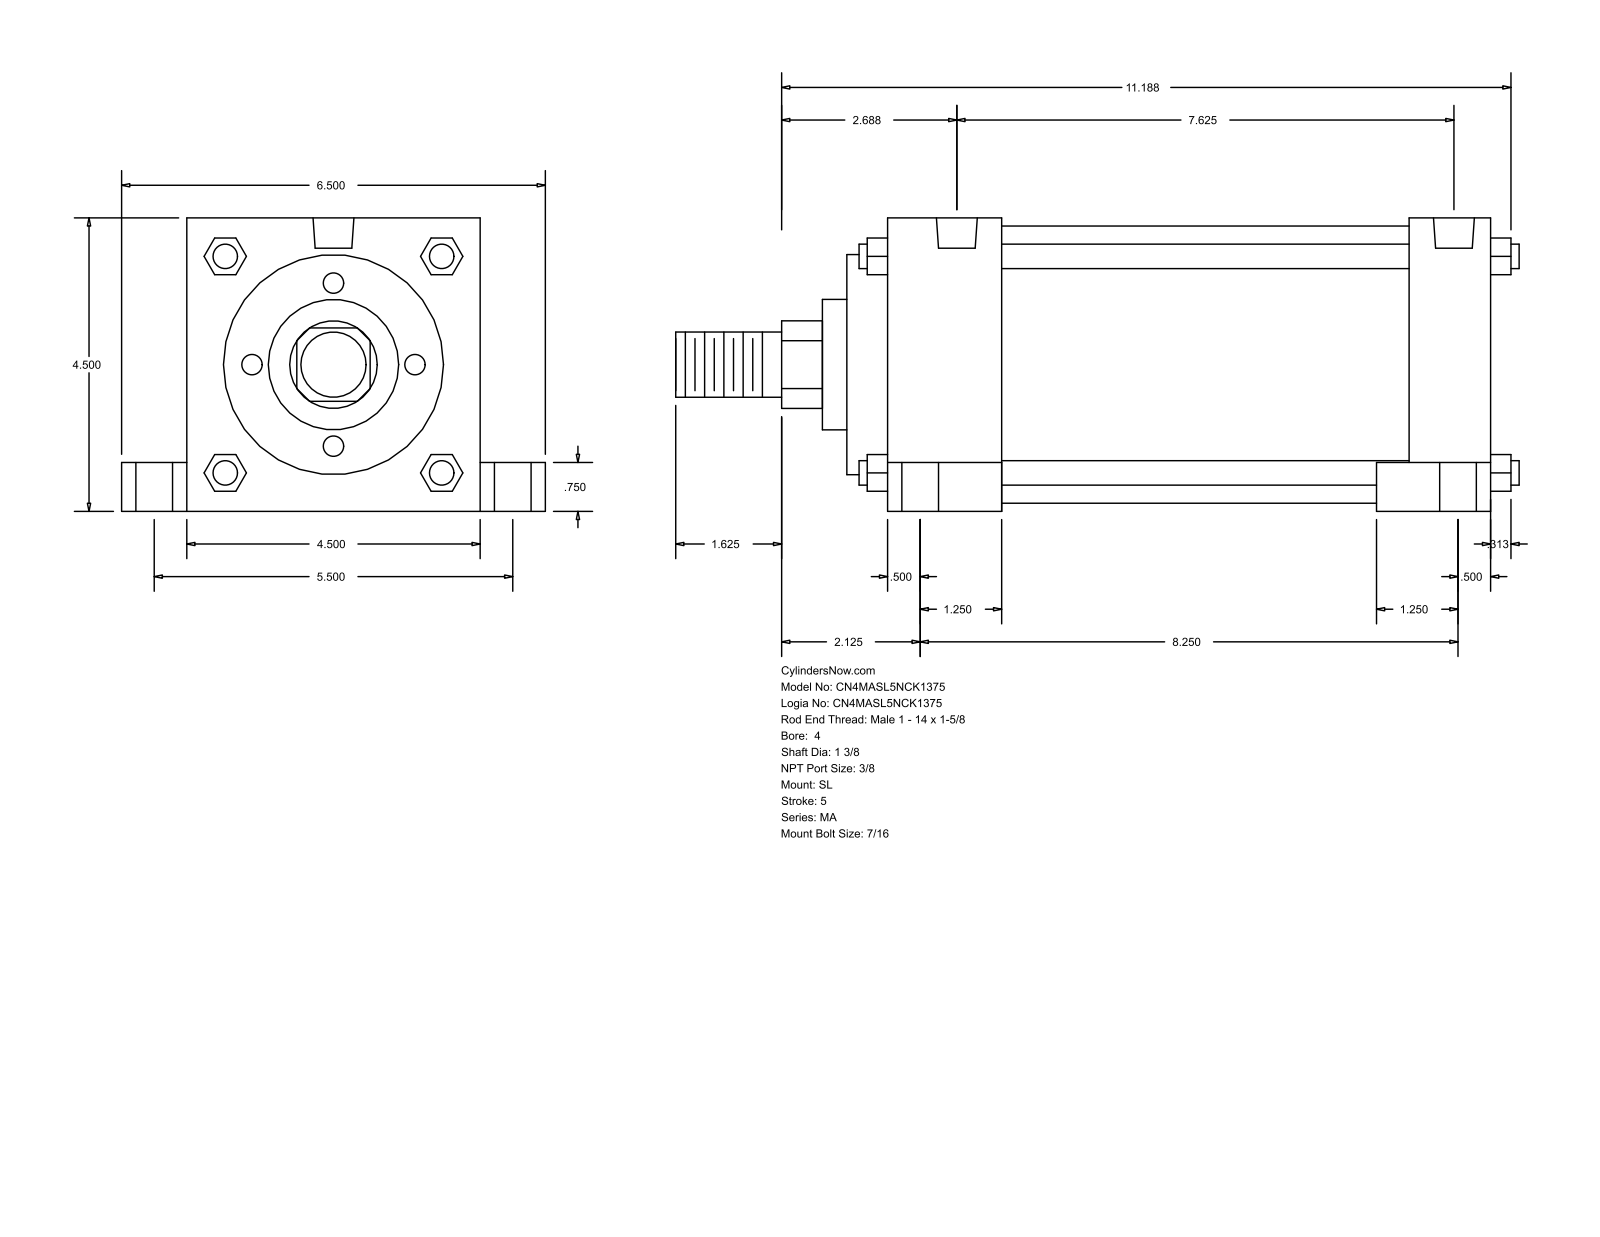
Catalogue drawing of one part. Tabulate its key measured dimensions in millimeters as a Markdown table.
| quantity | value |
| --- | --- |
| part name | MA_SL__0400_1.375 |
| STEP written by | GSSL Pune (CONFIG_CONTROL_DESIGN) |
| units | millimeters |
| bodies | 0 solids, 150 faces (113 planar, 37 cylindrical, 0 other) |
| overall size | 328.61 × 165.1 × 114.3 |
| round holes (diameter × count) | 11.11 × 4, 14.29 × 4, 20.64 × 4, 15.93 × 2 |
| round bosses / shafts (diameter × count) | 9.53 × 4, 107.95 × 1, 85.72 × 1, 50.8 × 1, 34.92 × 1, 25.4 × 1 |
| partial cylindrical surfaces (radius × count) | 17.06 × 1 |
| main face-to-face distances | 114.3, 234.96, 158.75, 15.87, 250.83, 60.32, 44.45, 190.51, 219.07, 203.2 |
| hole center spacings | 69.87, 70.14, 71.29, 72.4, 139.7, 184.15, 202.89, 207.38 |
